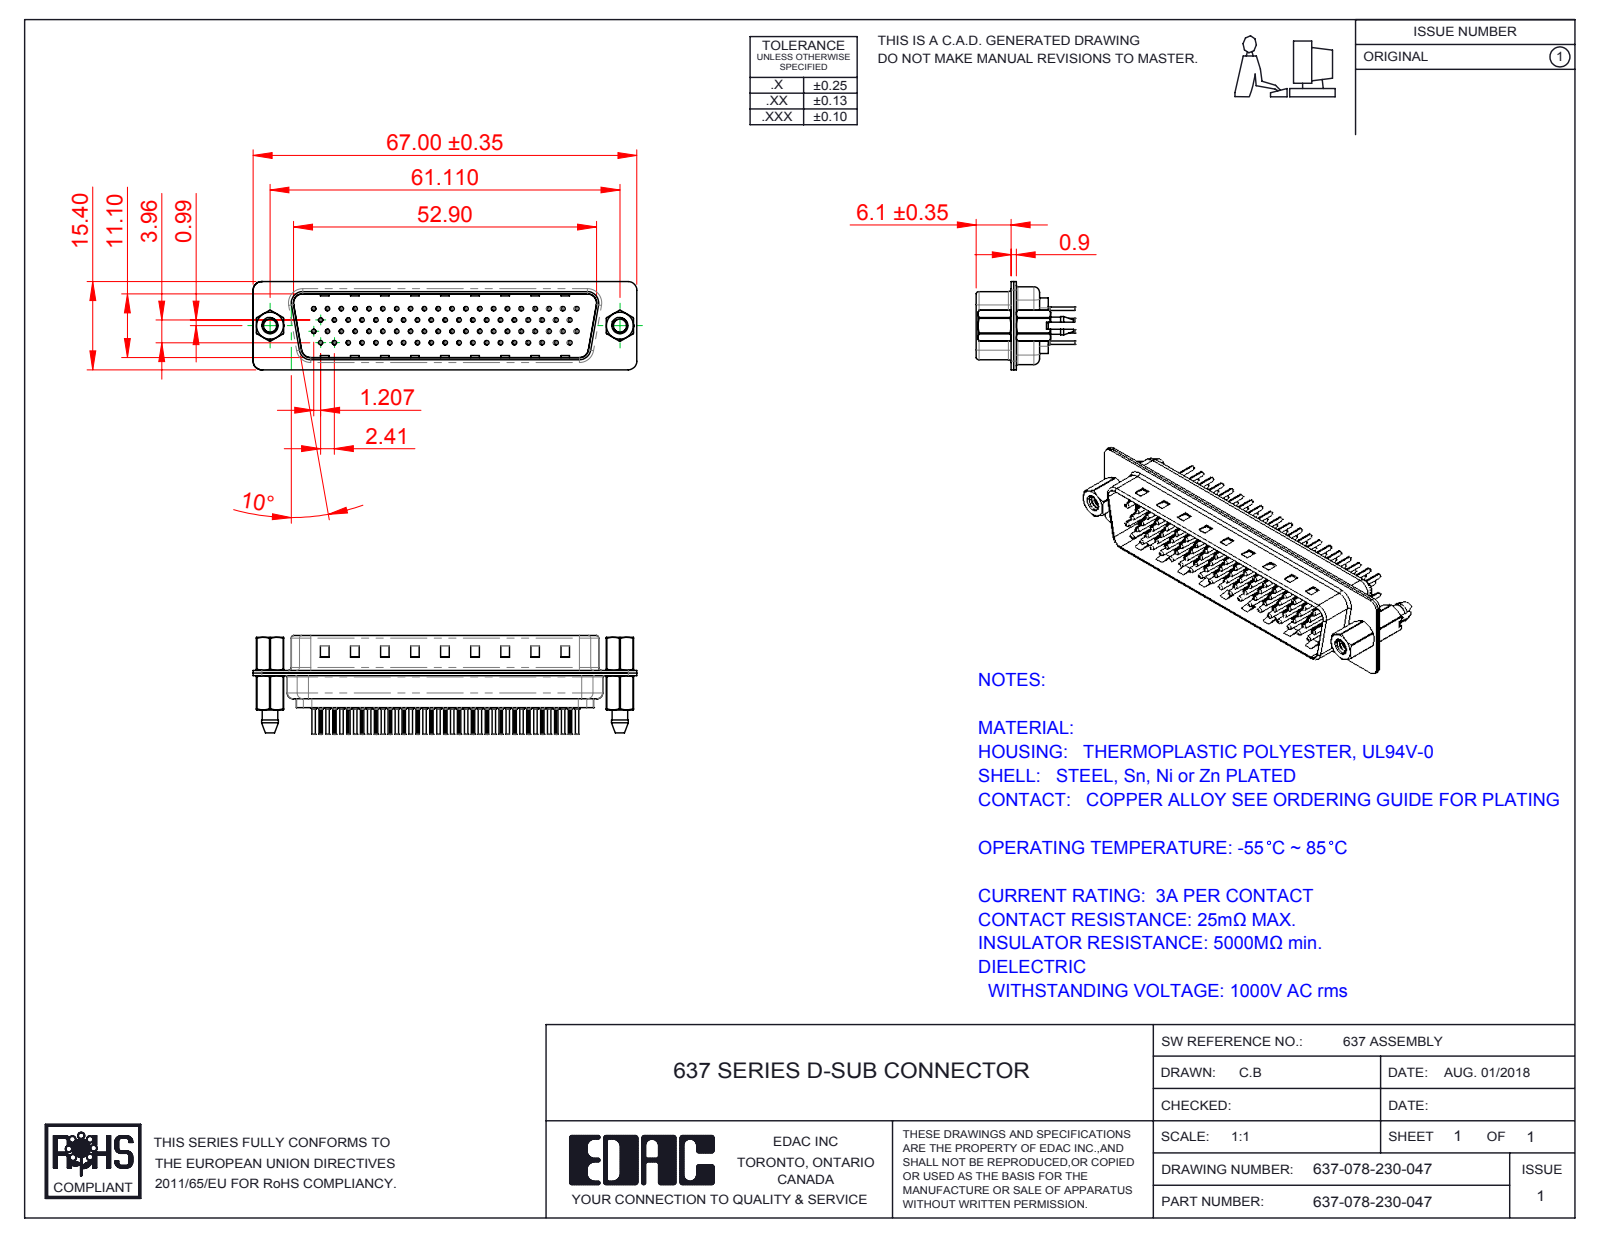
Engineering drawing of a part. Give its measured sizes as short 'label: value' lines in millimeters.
name: 637 Shell Front_78 Contacts; 637 Contact Row 78_30; 637 Housing_78 Contacts; 637 Contact Row 3_30 (+6 more)
written by: SolidWorks 2016 (CONFIG_CONTROL_DESIGN)
unit: mm
bodies: 85 solids, 8412 faces (2129 planar, 3131 cylindrical, 3152 other)
size: 67 × 17.25 × 15.4
volume: 4 660 mm³; area: 16 633 mm²
holes: 150× ⌀1.6, 78× ⌀0.2, 78× ⌀0.35, 78× ⌀1.1, 72× ⌀0.75, 72× ⌀2, 3× ⌀4, 2× ⌀2.26, 2× ⌀2.29, 2× ⌀4.8
bosses: 78× ⌀2, 78× ⌀1.5, 78× ⌀0.75, 78× ⌀0.6, 2× ⌀4.9, 2× ⌀2.79, 1× ⌀4.8
rounds: 156× R0.1, 18× R1.5, 12× R2, 8× R0.5, 6× R1.6, 4× R0.25, 4× R0.55, 4× R0.7
face distances: 0.45, 0.4, 1.95, 1.5, 11.9, 11.5, 0.7, 11.1, 0.9, 0.8
hole spacings: 2.41, 7.24, 6.06, 9.65, 6.96, 8.46, 14.54, 16.89
